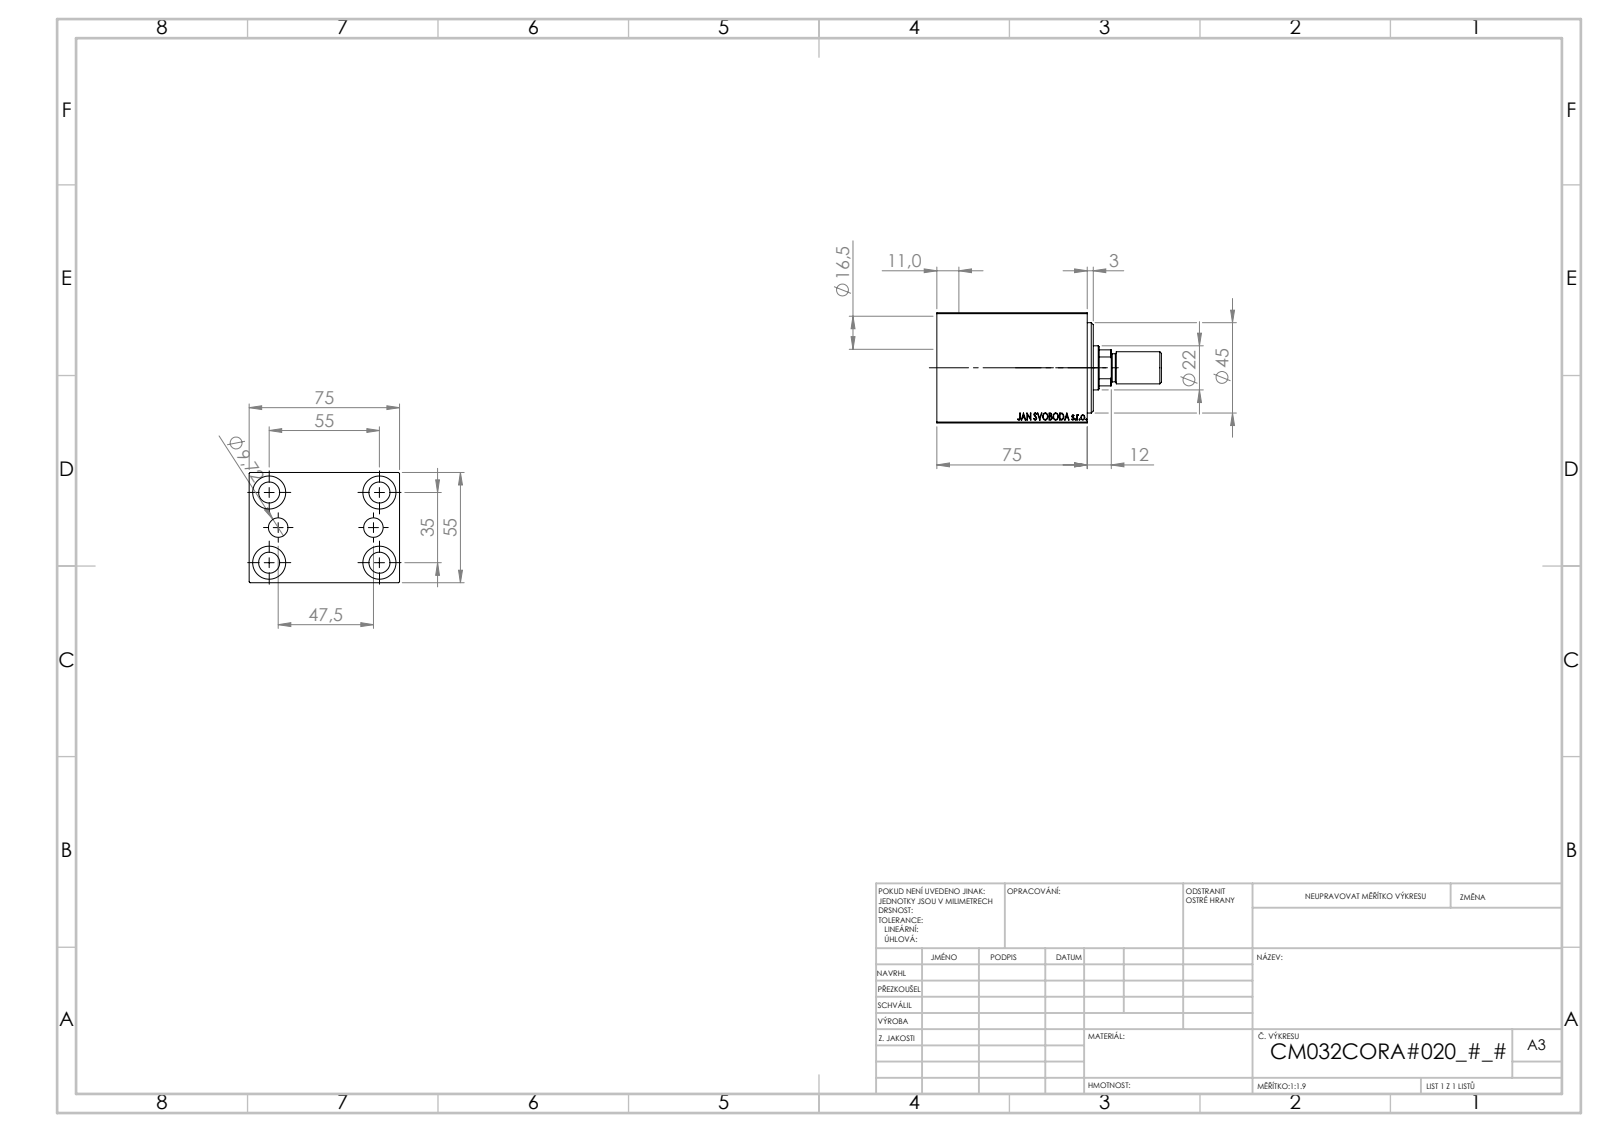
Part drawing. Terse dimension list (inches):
name: V450CM_C_Body; V450CM_C_VCP; V450CM_MALE_METRIC; V450CM_VC_B
written by: SolidWorks 2019 (CONFIG_CONTROL_DESIGN)
unit: in
bodies: 4 solids, 871 faces (411 planar, 60 cylindrical, 400 other)
size: 4.409 × 2.953 × 2.165
volume: 16.56 in³; area: 100.4 in²
holes: 5× ⌀0.413, 4× ⌀0.65, 2× ⌀0.157, 2× ⌀0.383, 1× ⌀0.866, 1× ⌀1.004, 1× ⌀1.26, 1× ⌀1.339, 1× ⌀1.772
bosses: 1× ⌀0.63, 1× ⌀0.551
rounds: 1× R0.413
face distances: 2.953, 2.165, 0.394, 2.559, 2.756, 0.197, 2.362, 0.433, 2.52, 0.118
hole spacings: 0.705, 1.283, 2.132, 0.935, 1.378, 2.165, 2.567, 1.87
